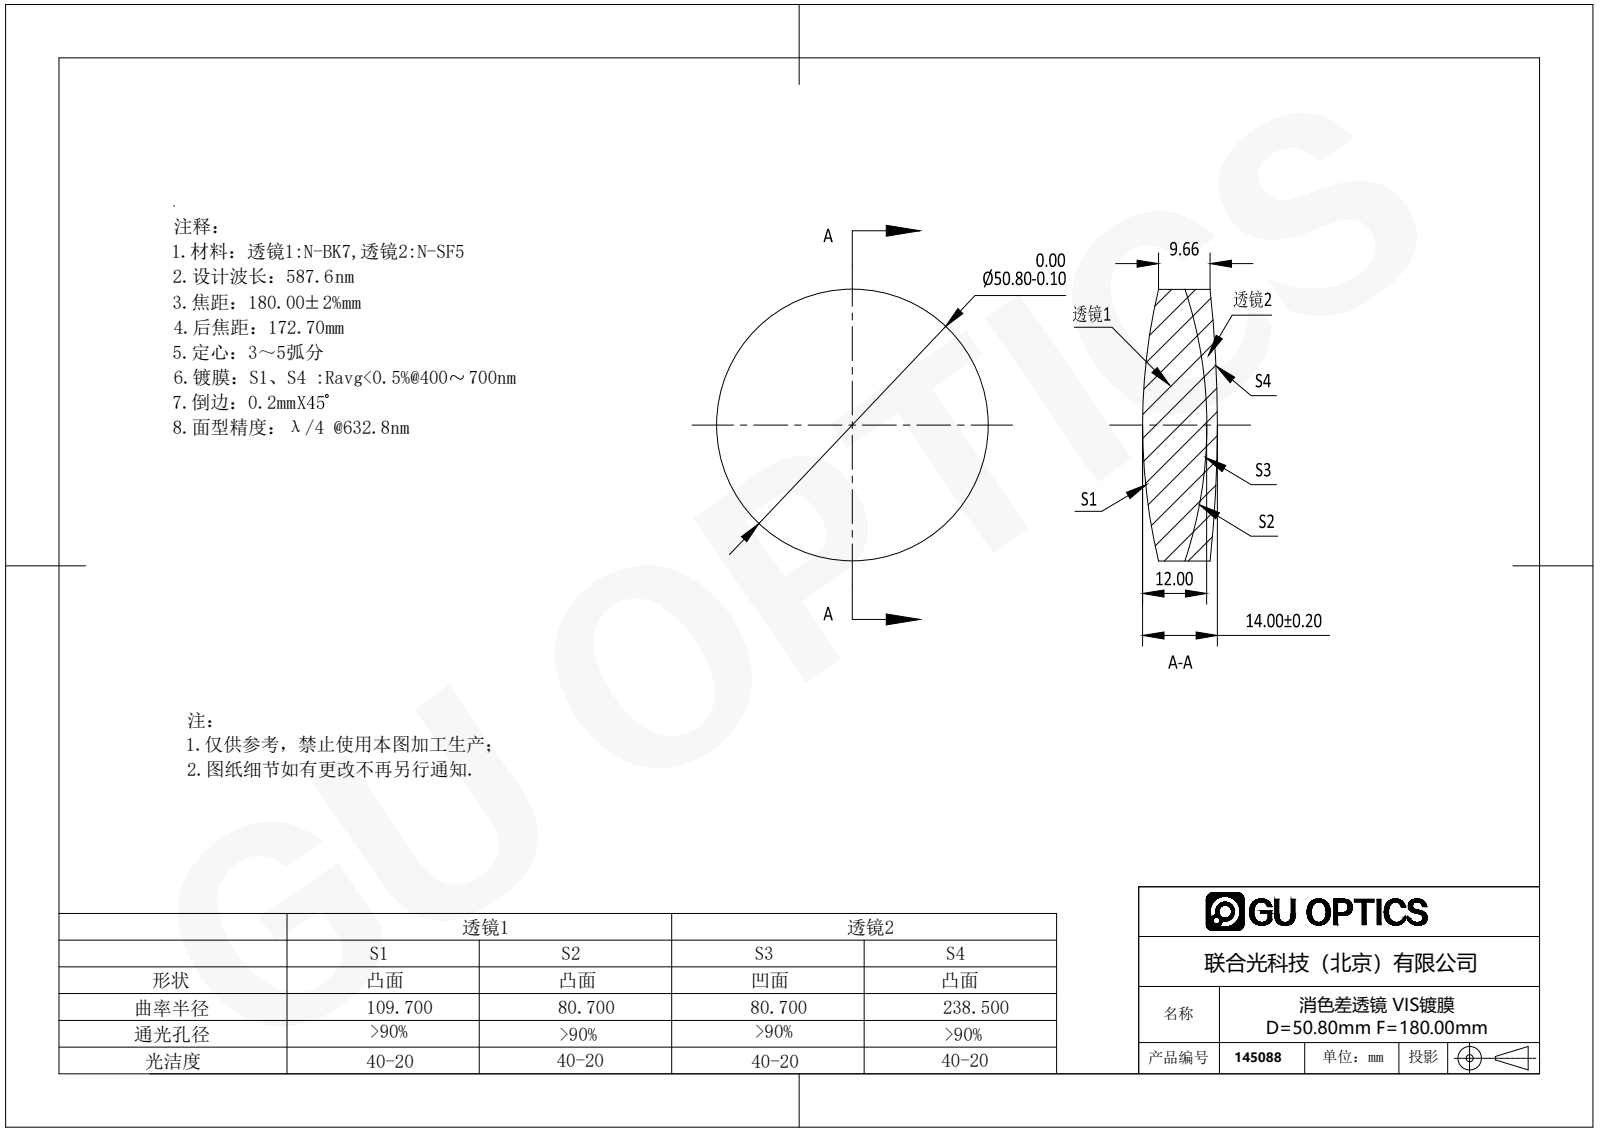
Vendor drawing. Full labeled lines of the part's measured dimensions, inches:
Part name (STEP PRODUCT): 145088
STEP written by: SolidWorks 2016 (AUTOMOTIVE_DESIGN)
Units: inches
Bodies: 2 solids, 12 faces (0 planar, 4 cylindrical, 8 other)
Overall size (bounding box): 2 × 2 × 0.551
Volume: 1.464 in³ · Surface area: 15.17 in²
Round bosses / shafts (diameter × count): ⌀2 ×1
